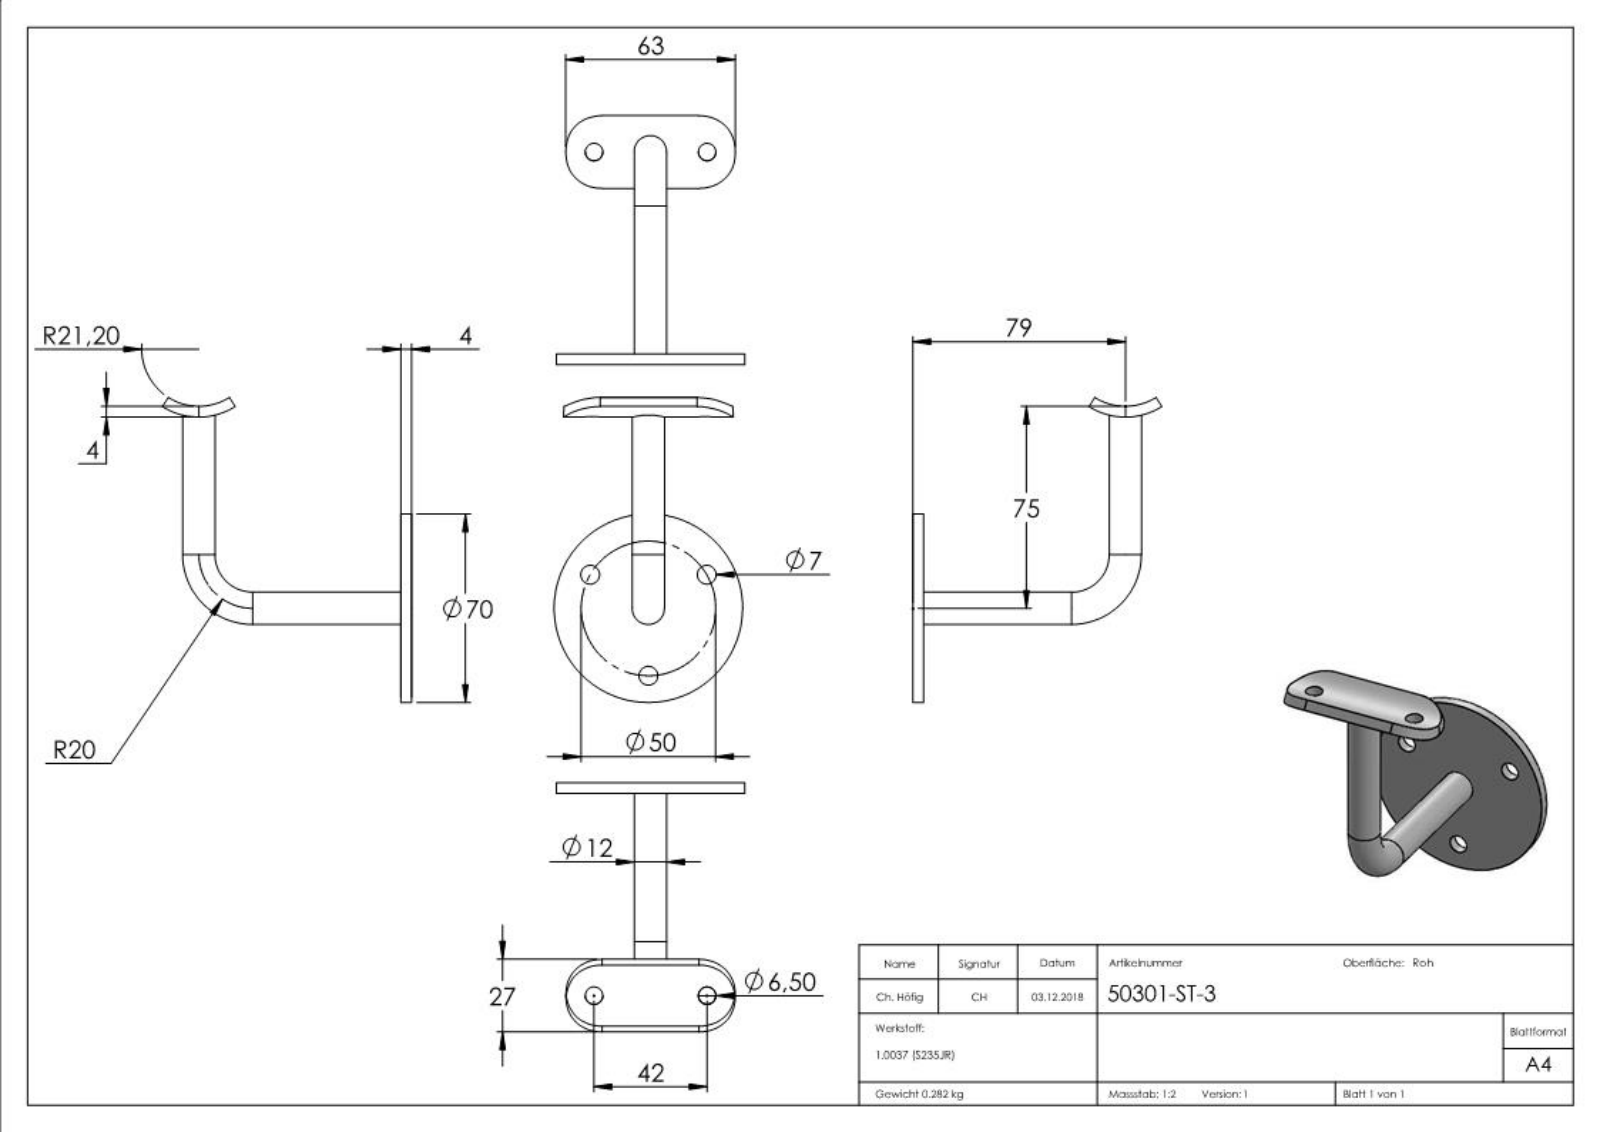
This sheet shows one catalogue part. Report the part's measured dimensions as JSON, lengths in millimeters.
{"part_name": "50301-ST-3", "step_written_by": "SolidWorks 2015 (CONFIG_CONTROL_DESIGN)", "units": "millimeters", "bodies": {"solids": 1, "faces": 258, "planar": 117, "cylindrical": 22, "other": 119}, "overall_size": [113.3, 92.5, 70], "volume_mm3": 36200, "surface_area_mm2": 17265, "round_holes": [[7, 3], [6.5, 2]], "round_bosses_or_shafts": [[12, 2], [70, 1]], "partial_cylinders_radius": [[13.5, 4], [21.2, 1], [25.2, 1]], "face_to_face_distances": [4, 0.5, 3.5, 0.67, 0.54, 0.66, 0.8, 1.33, 0.79, 0.72], "hole_center_spacings": [43.3, 42]}
